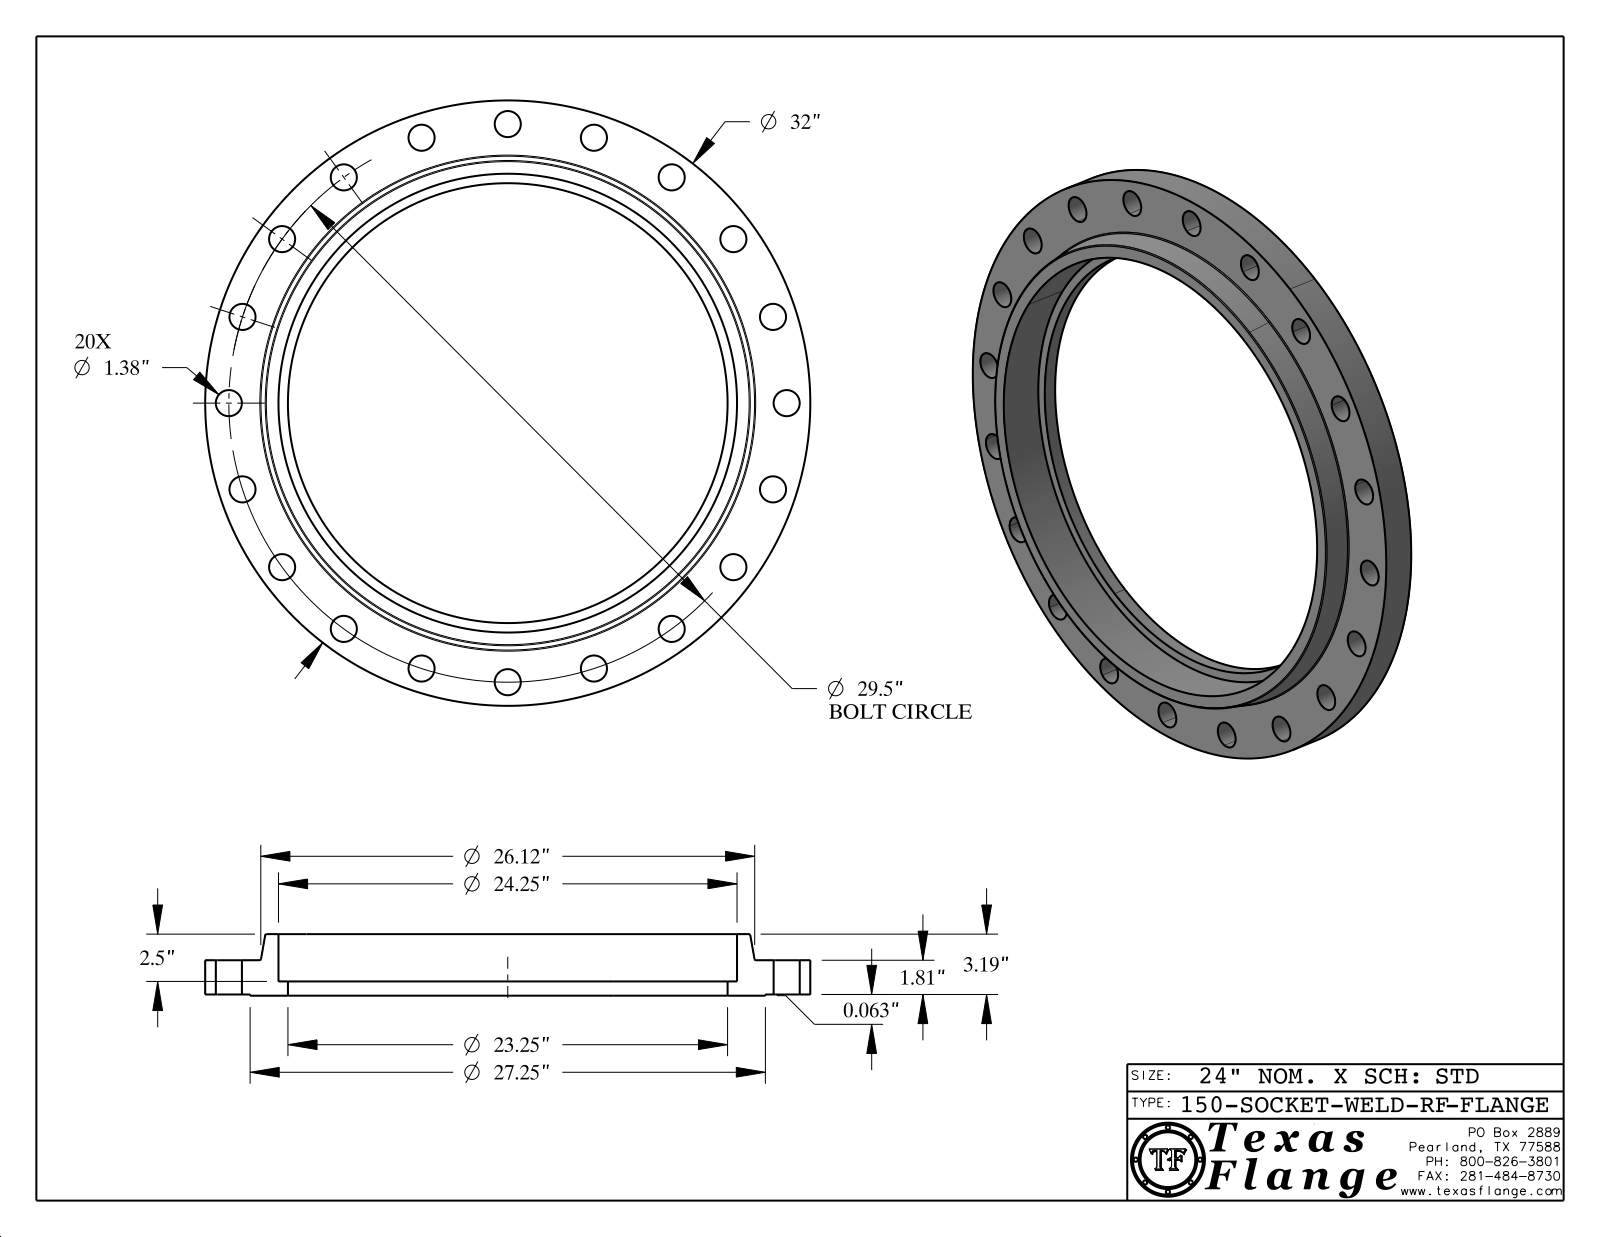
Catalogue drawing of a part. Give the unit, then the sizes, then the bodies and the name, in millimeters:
Units: millimetres
Overall size (bounding box): 812.8 × 812.8 × 82.6
Round holes (diameter × count): ⌀35.1 ×20, ⌀12.6 ×1, ⌀590.6 ×1, ⌀616 ×1
Round bosses / shafts (diameter × count): ⌀0.8 ×8, ⌀812.8 ×1, ⌀692.2 ×1, ⌀9.9 ×1
Main face-to-face distances: 46, 1.6, 47.5, 82.6, 81, 35.1, 19.1, 17.5, 28.4, 63.5
Hole centre spacings: 374.7, 740.1, 117.2, 440.4, 529.8, 606.2, 667.6, 231.5
Volume: 11 300 000 mm³ · Surface area: 891 000 mm²
Bodies: 1 solid, 444 faces (370 planar, 68 cylindrical, 6 other)
Part name (STEP PRODUCT): 150-SOCKET-WELD-RF
STEP written by: CATIA V5 STEP AP214 (AUTOMOTIVE_DESIGN)
